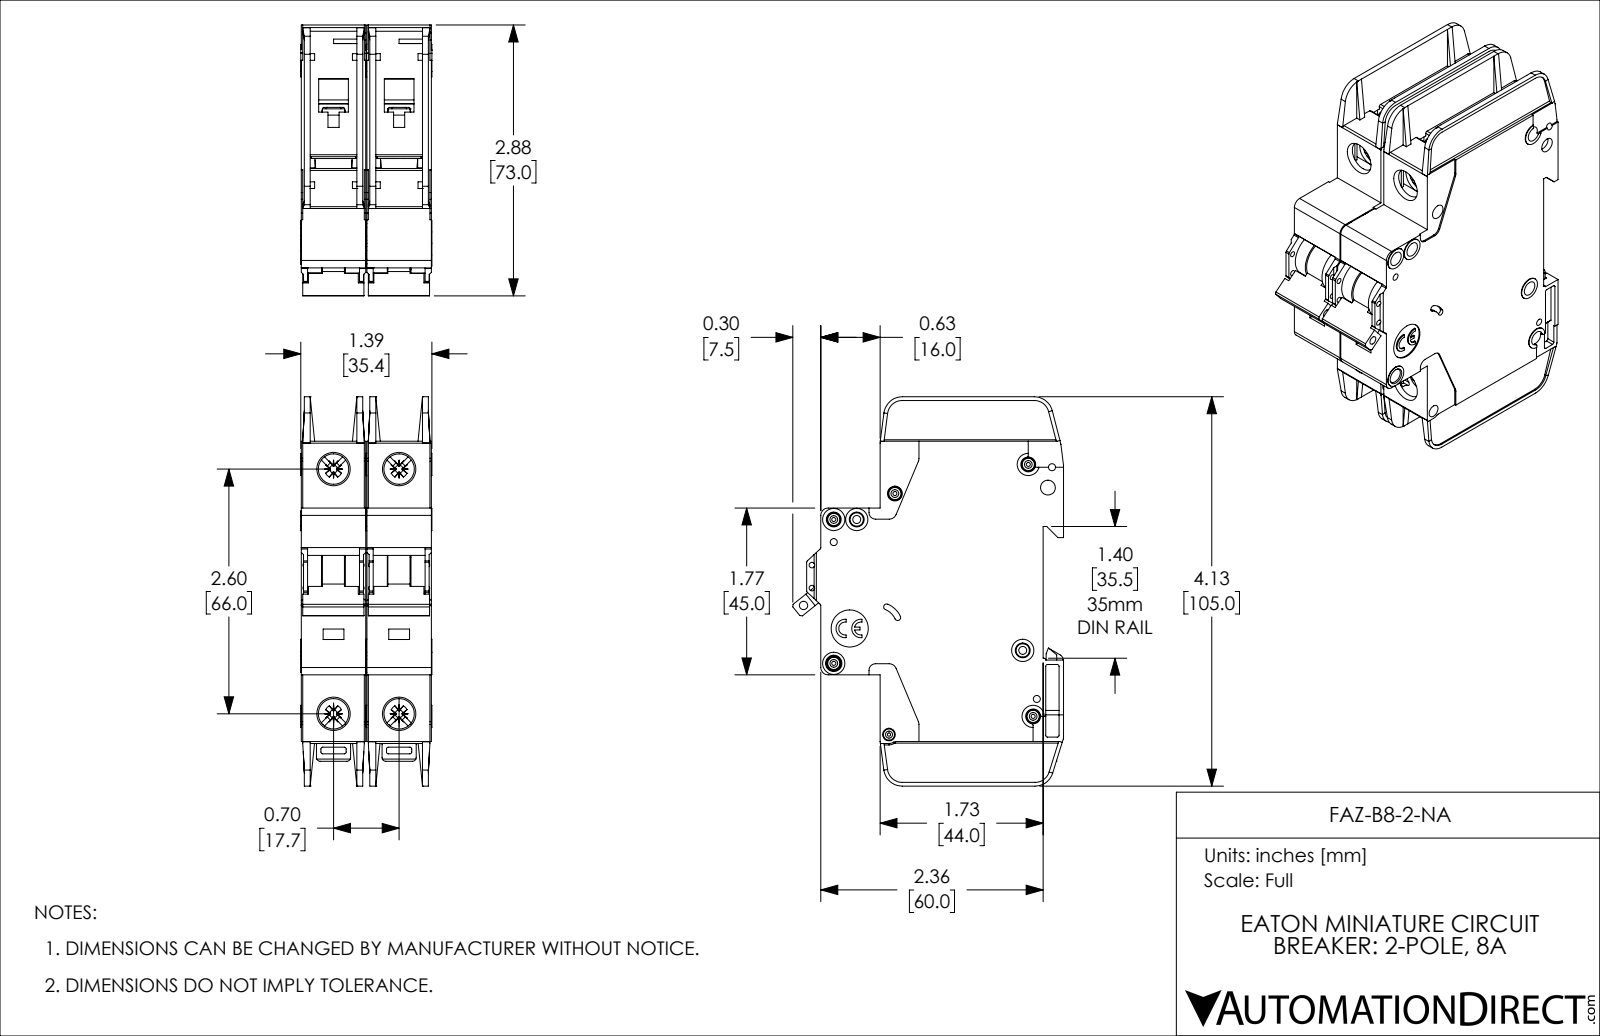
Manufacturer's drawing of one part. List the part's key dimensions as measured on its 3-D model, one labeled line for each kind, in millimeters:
Part name (STEP PRODUCT): FAZ-B8-2-NA
STEP written by: SolidWorks 2019 (AUTOMOTIVE_DESIGN)
Units: millimetres
Bodies: 2 solids, 2254 faces (1342 planar, 714 cylindrical, 198 other)
Overall size (bounding box): 105 × 73.1 × 35.4
Volume: 153 500 mm³ · Surface area: 52 910 mm²
Round holes (diameter × count): ⌀4 ×8, ⌀1.1 ×5, ⌀1.9 ×4, ⌀8.2 ×4, ⌀1.5 ×2, ⌀2.2 ×2, ⌀0.9 ×1, ⌀2.3 ×1, ⌀2.5 ×1, ⌀3.4 ×1, ⌀10 ×1
Round bosses / shafts (diameter × count): ⌀3.3 ×5, ⌀6 ×4, ⌀3 ×3, ⌀2.5 ×2
Partial cylindrical surfaces — rounded edges, fillets, slot ends (radius × count): R0.5 ×57, R0.4 ×20, R1 ×14, R2 ×10, R1.1 ×8, R0.2 ×5, R5 ×5, R0.3 ×4
Main face-to-face distances: 17.7, 1.2, 17.4, 15, 2.4, 16.2, 13.8, 35.1, 18.9, 16.5
Hole centre spacings: 6.2, 13.6, 17.7, 22.1, 66, 68.3, 4.8, 5.1
